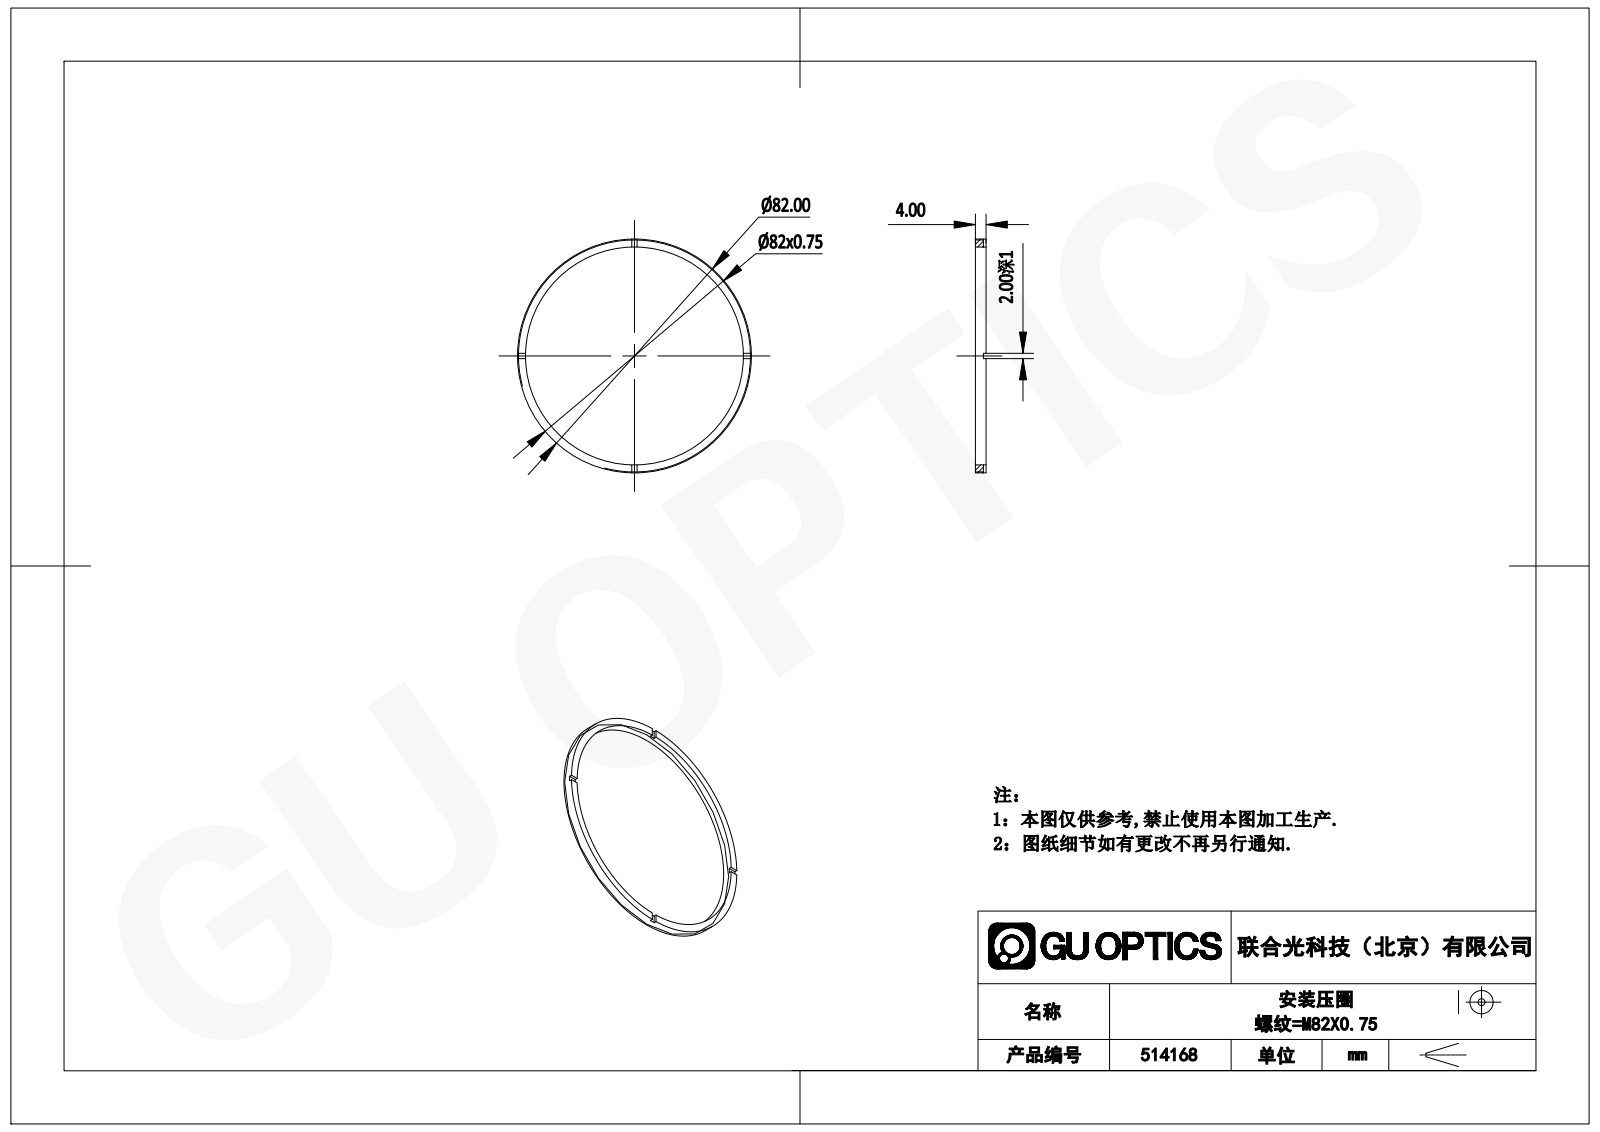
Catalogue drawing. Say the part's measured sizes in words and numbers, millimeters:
The part is named "514168". Its 3-D file was written by "SolidWorks 2020 (CONFIG_CONTROL_DESIGN)". It is 1 solid with 21 faces: 17 planar, 4 cylindrical and 0 other. Overall it measures 82 by 82 by 4 millimeters. Its volume is 2 954 cubic millimeters and its surface area 3 483 square millimeters. Round holes: 1 of diameter 76. Round bosses or shafts: 1 of diameter 82. The main face-to-face distances are 4, 3, 1, 2.
